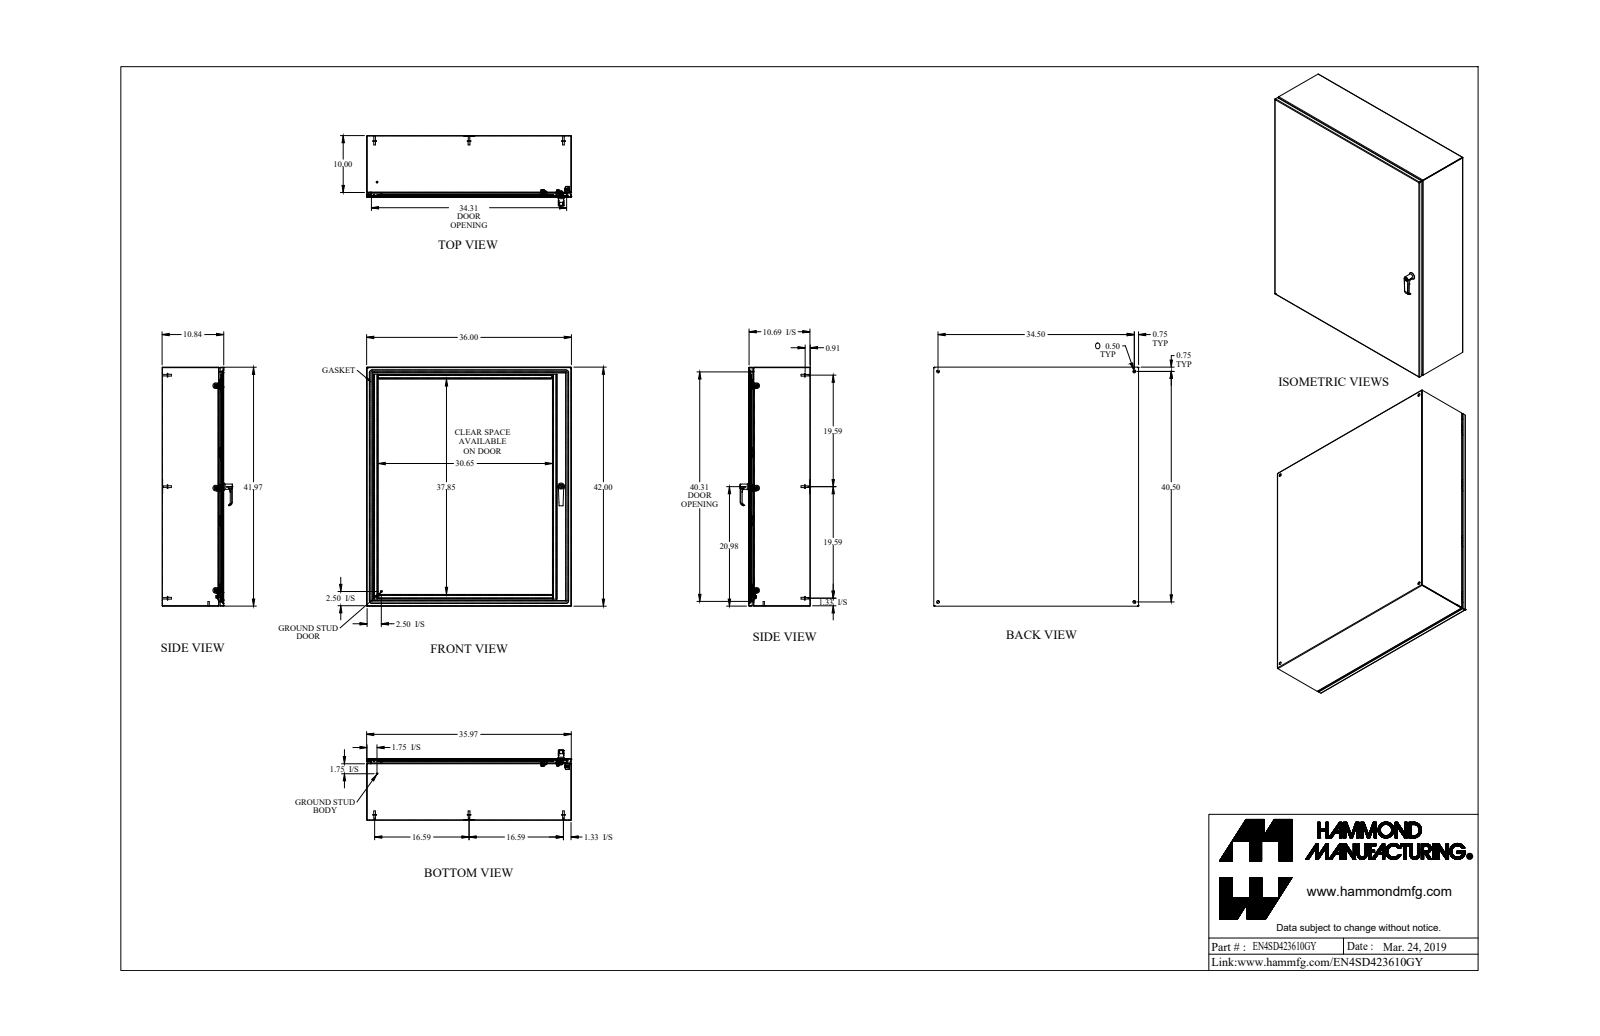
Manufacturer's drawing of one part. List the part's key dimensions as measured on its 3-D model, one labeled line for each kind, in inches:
Part name (STEP PRODUCT): EN4SD423610GY
STEP written by: SolidWorks 2019 (AUTOMOTIVE_DESIGN)
Units: inches
Bodies: 61 solids, 1733 faces (757 planar, 638 cylindrical, 338 other)
Overall size (bounding box): 42 × 36 × 12.367
Volume: 386.7 in³ · Surface area: 10 815 in²
Round holes (diameter × count): ⌀0.176 ×6, ⌀0.196 ×4, ⌀0.5 ×4, ⌀0.25 ×3, ⌀0.265 ×3, ⌀0.413 ×3, ⌀0.256 ×2, ⌀0.313 ×2, ⌀0.394 ×2, ⌀0.172 ×1, ⌀0.24 ×1, ⌀0.242 ×1
Round bosses / shafts (diameter × count): ⌀0.313 ×8, ⌀0.27 ×8, ⌀0.25 ×7, ⌀0.625 ×6, ⌀0.375 ×6, ⌀0.156 ×6, ⌀1 ×3, ⌀0.625 ×3
Partial cylindrical surfaces — rounded edges, fillets, slot ends (radius × count): R0.043 ×24, R0.081 ×24, R0.036 ×20, R0.108 ×20, R0.03 ×15, R0.062 ×12, R0.094 ×10, R0.016 ×9
Main face-to-face distances: 0.072, 10.765, 10.693, 10.837, 35.928, 41.928, 35.856, 36, 41.856, 42
Hole centre spacings: 0.787, 2.507, 17.981, 17.988, 18, 33.504, 34.5, 35.969
